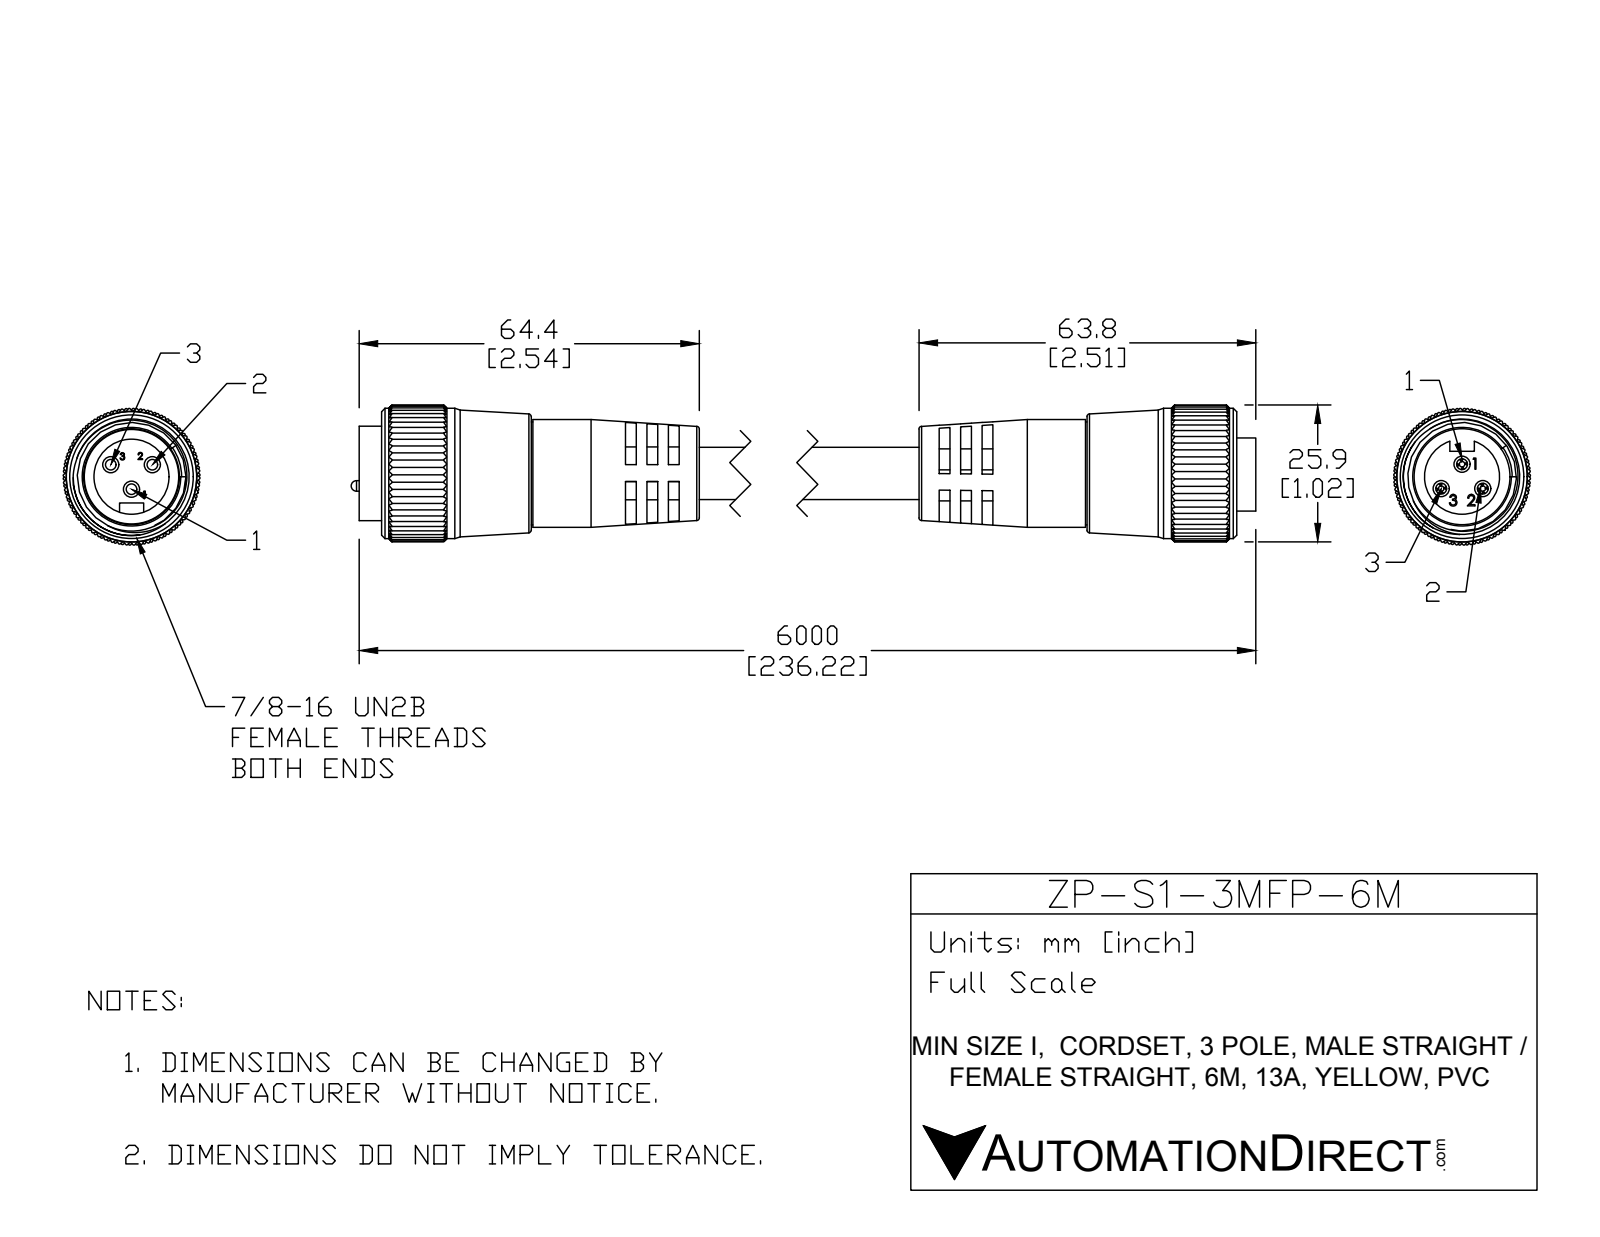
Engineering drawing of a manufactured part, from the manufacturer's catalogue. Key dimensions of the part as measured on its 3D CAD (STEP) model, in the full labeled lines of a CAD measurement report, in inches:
Part name (STEP PRODUCT): ZP-S1-3MFP-6M
STEP written by: SolidWorks 2015 (AUTOMOTIVE_DESIGN)
Units: inches
Bodies: 7 solids, 1099 faces (389 planar, 618 cylindrical, 92 other)
Overall size (bounding box): 9.042 × 1.017 × 1.017
Volume: 3.1 in³ · Surface area: 36.17 in²
Round holes (diameter × count): ⌀0.12 ×3, ⌀0.786 ×1, ⌀0.805 ×1, ⌀0.827 ×1
Round bosses / shafts (diameter × count): ⌀0.12 ×3, ⌀0.079 ×3, ⌀0.972 ×1, ⌀0.803 ×1, ⌀0.768 ×1, ⌀0.704 ×1, ⌀0.56 ×1, ⌀0.39 ×1
Partial cylindrical surfaces — rounded edges, fillets, slot ends (radius × count): R0.01 ×165, R0.09 ×1, R0.207 ×1, R0.509 ×1
Main face-to-face distances: 0.079, 0.158, 4.633, 4.474, 0.159, 4.95, 2.356, 0.159, 4.791, 4.792
Hole centre spacings: 0.239, 0.093, 0.178, 0.179, 0.31
